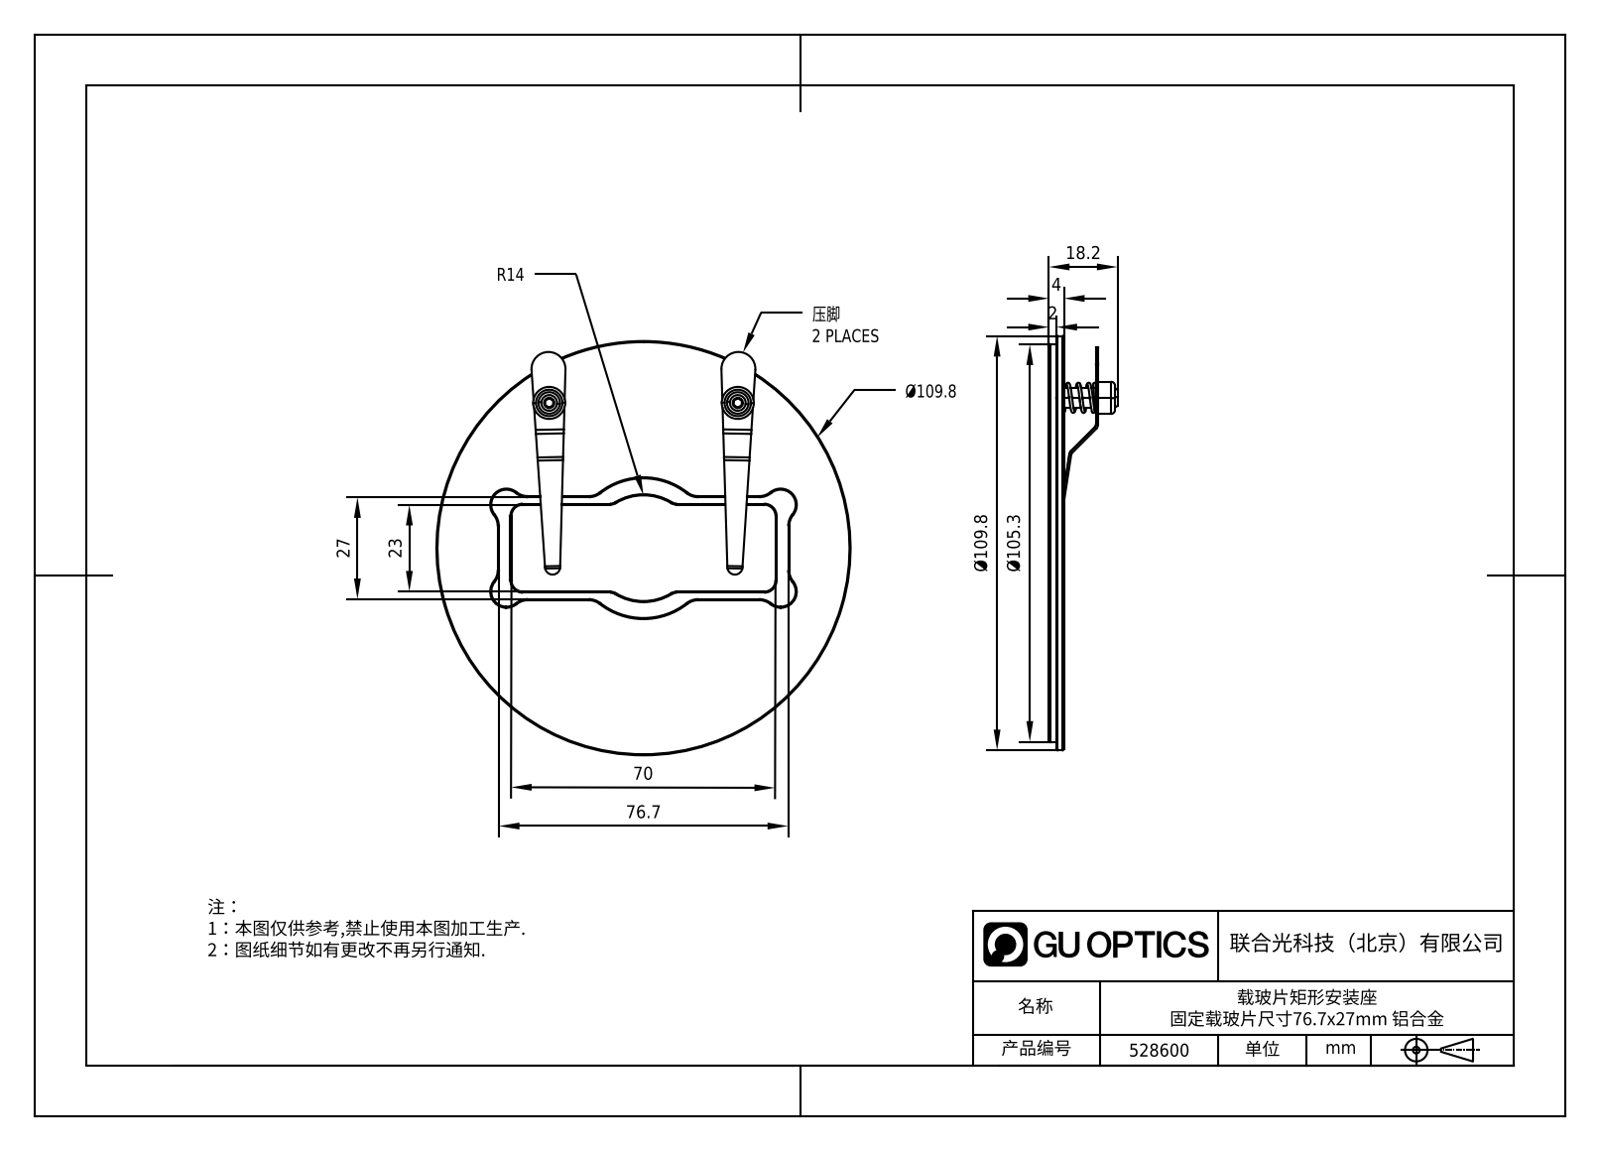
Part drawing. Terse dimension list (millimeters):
name: 蘑菇头内六角螺丝，A_LM3*16; 耳8x12-0.8; CFZ-C2676; 32.6.14_QY-YD-6_6mm压脚（带螺纹）单片 (+2 more)
written by: SolidWorks 2021 (CONFIG_CONTROL_DESIGN)
unit: mm
bodies: 7 solids, 245 faces (88 planar, 80 cylindrical, 77 other)
size: 109.8 × 109.8 × 18.2
volume: 29 021 mm³; area: 21 166 mm²
holes: 2× ⌀2.5, 2× ⌀3.2, 2× ⌀7
bosses: 2× ⌀8.5, 2× ⌀5.3, 2× ⌀3, 1× ⌀109.8, 1× ⌀105.3
rounds: 12× R1.5, 12× R5, 8× R3, 4× R4, 2× R2, 2× R4.5, 1× R14, 1× R18.5
face distances: 4, 2, 1, 0.5, 3, 12.5, 11.5, 10.5, 8.5, 12
hole spacings: 50
